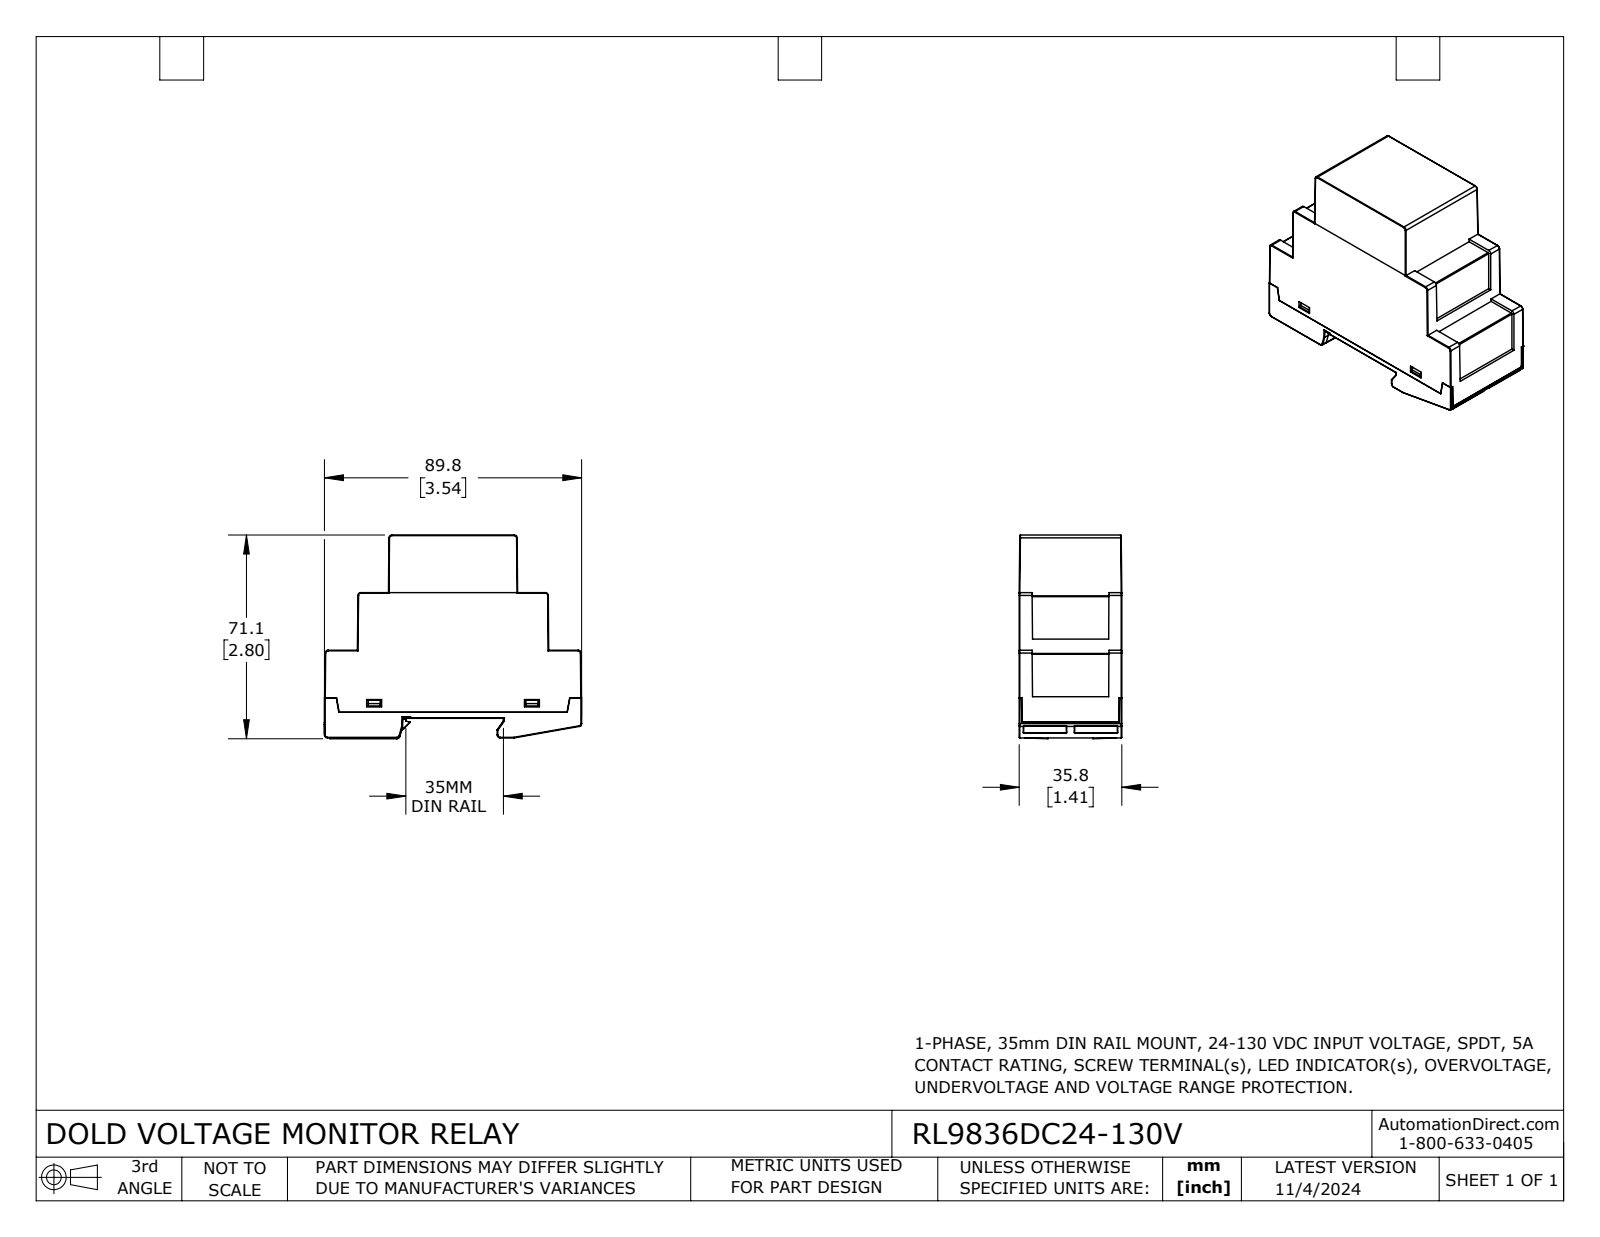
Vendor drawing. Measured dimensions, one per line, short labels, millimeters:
name: RL9836DC24-130V
written by: SolidWorks 2023 (CONFIG_CONTROL_DESIGN)
unit: mm
bodies: 2 solids, 631 faces (484 planar, 109 cylindrical, 38 other)
size: 89.9 × 71.1 × 35.8
volume: 153 100 mm³; area: 35 650 mm²
bosses: 2× ⌀2.5, 1× ⌀8
rounds: 42× R0.2, 14× R1, 11× R0.5, 6× R0.1, 4× R0.3, 1× R0.3, 1× R0.4, 1× R0.7
face distances: 35.8, 5.5, 64, 0.9, 2.2, 61.8, 56.4, 7.6, 20.9, 34.9
